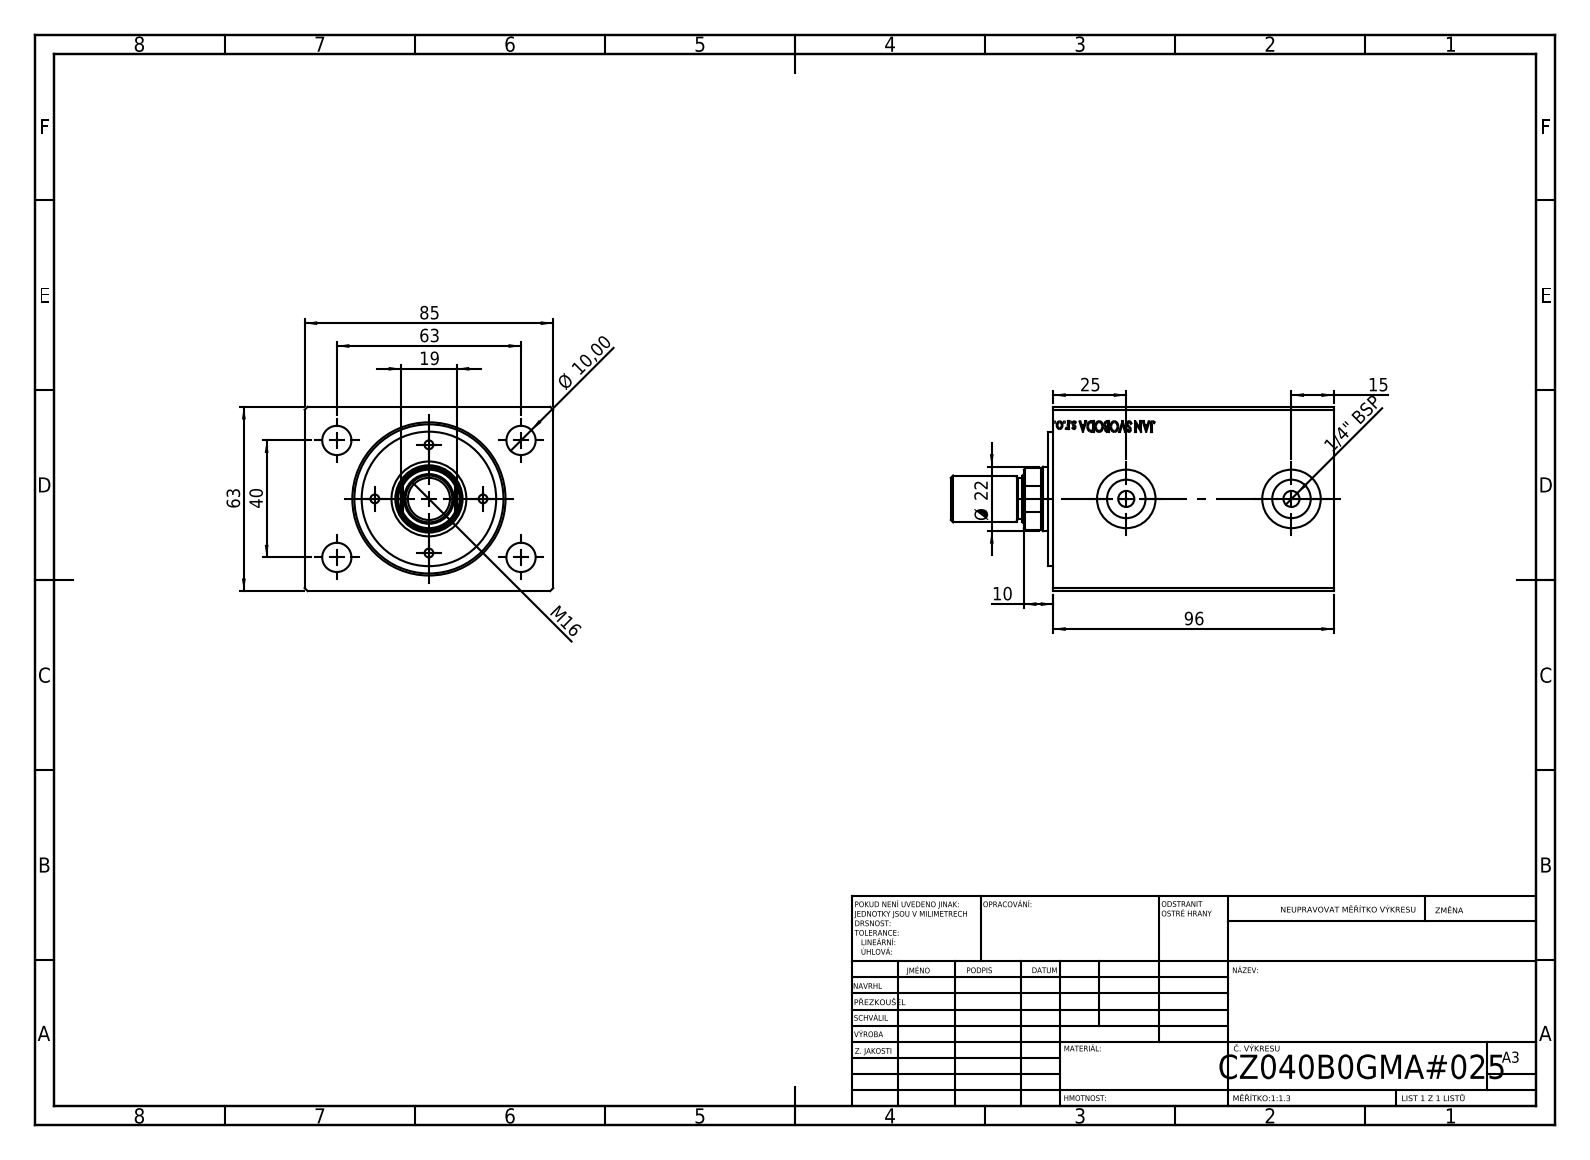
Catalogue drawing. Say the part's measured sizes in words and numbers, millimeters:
The part is named "V500CZ_MALE_METRIC; V500CZ_B_VC; V500CZ". Its 3-D file was written by "SolidWorks 2019 (CONFIG_CONTROL_DESIGN)". It is 4 solids with 888 faces: 404 planar, 62 cylindrical and 422 other. Overall it measures 131 by 85 by 63 millimeters. Its volume is 475 090 cubic millimeters and its surface area 76 778 square millimeters. Round holes: 4 of diameter 3, 4 of diameter 10, 2 of diameter 5.5, 2 of diameter 13.16, 2 of diameter 20, 1 of diameter 14.5, 1 of diameter 22, 1 of diameter 23, 1 of diameter 36, 1 of diameter 40, 1 of diameter 51. Round bosses or shafts: 1 of diameter 46, 1 of diameter 16, 1 of diameter 14. Partial cylindrical surfaces (rounded edges, fillets, slot ends): 1 of radius 10.5. The main face-to-face distances are 63, 85, 96, 80.7, 15.3, 10, 8.2, 1.8, 72.5, 87.8. The hole center spacings are 18.5, 23.85, 26.16, 31.54, 37.31, 49.74, 53.85, 37.
